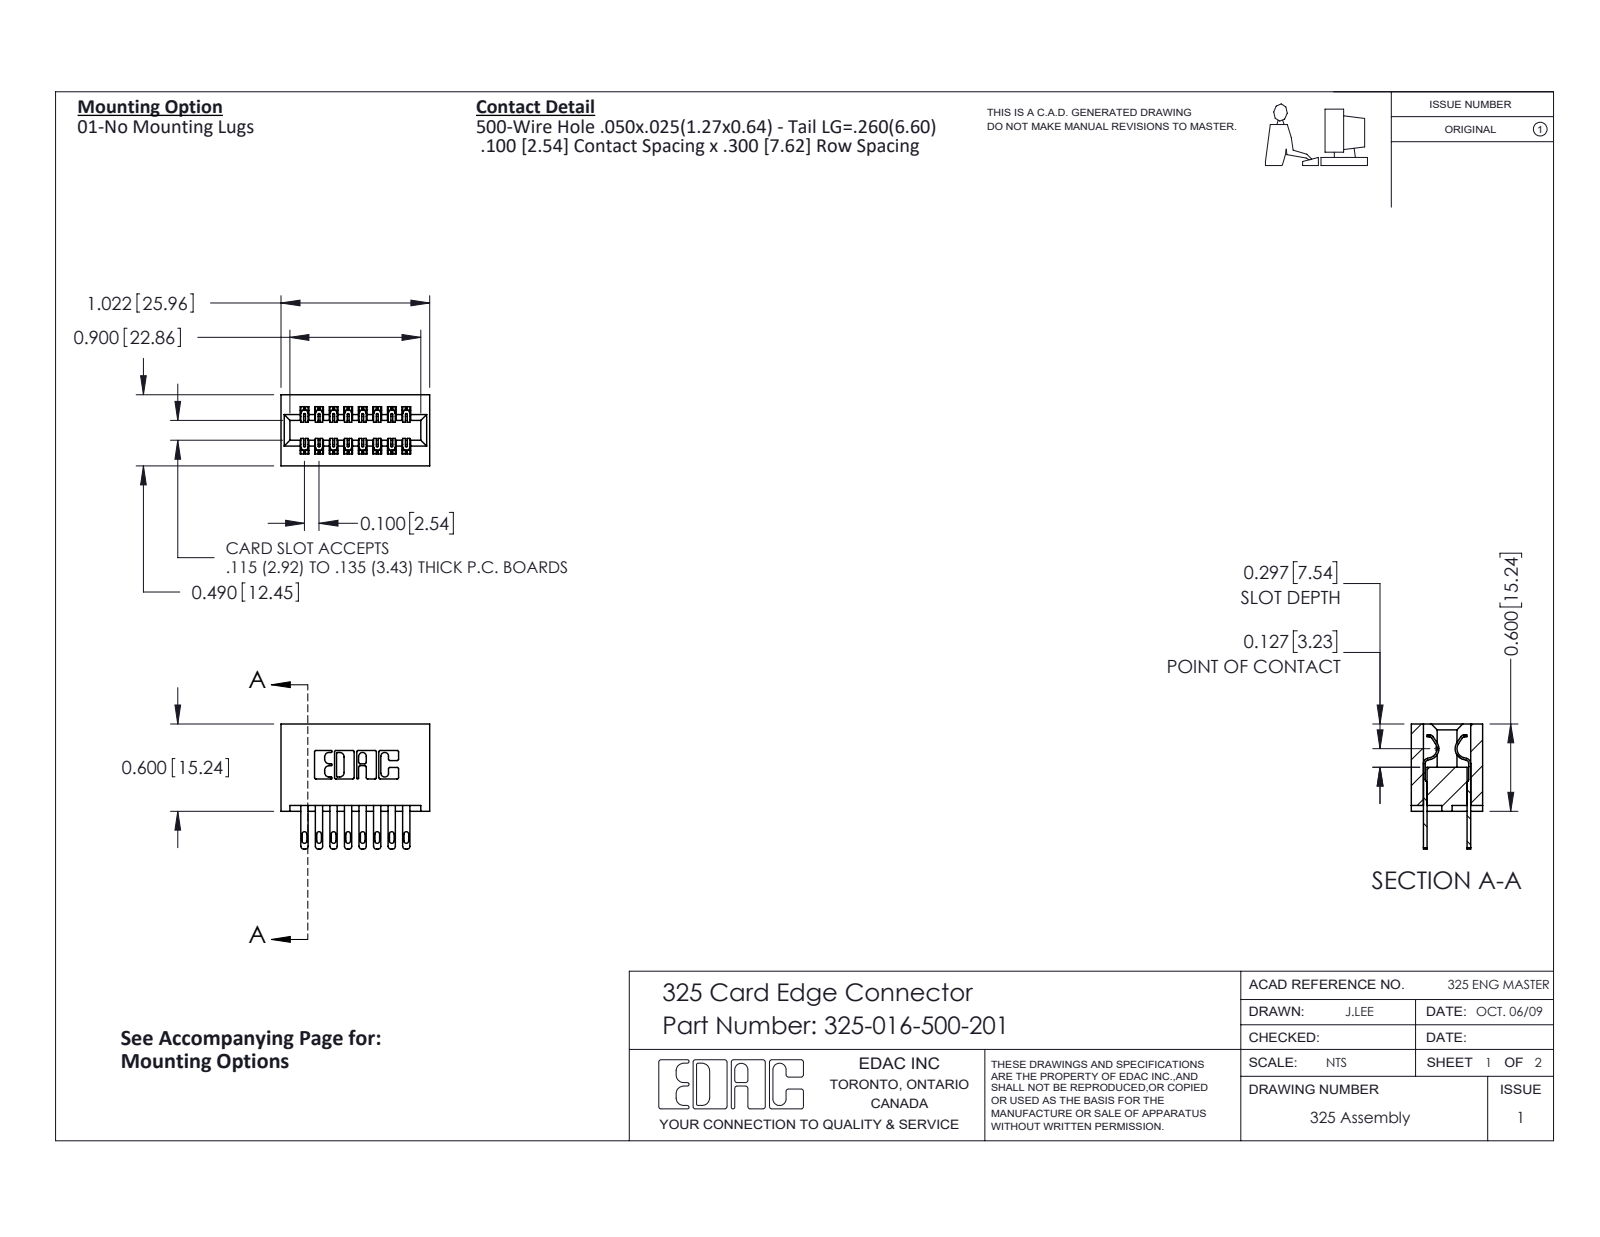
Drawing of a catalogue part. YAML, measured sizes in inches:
part_name: "325-292-001_325-293-100; 325-016-500-201; 325 Part_Lugless"
step_written_by: "SolidWorks 2016 (CONFIG_CONTROL_DESIGN)"
units: inches
bodies: {solids: 17, faces: 874, planar: 546, cylindrical: 328, other: 0}
overall_size: [1.022, 0.86, 0.49]
volume: 0.226
surface_area: 6.978
partial_cylinders:
  - {radius: 0.006, count: 24}
  - {radius: 0.01, count: 22}
  - {radius: 0.016, count: 16}
  - {radius: 0.02, count: 16}
  - {radius: 0.007, count: 6}
  - {radius: 0.031, count: 6}
  - {radius: 0.026, count: 3}
  - {radius: 0.014, count: 2}
face_to_face_distances: [0.3, 0.083, 0.407, 0.1, 0.2, 0.04, 0.107, 0.383, 0.025, 0.06]
